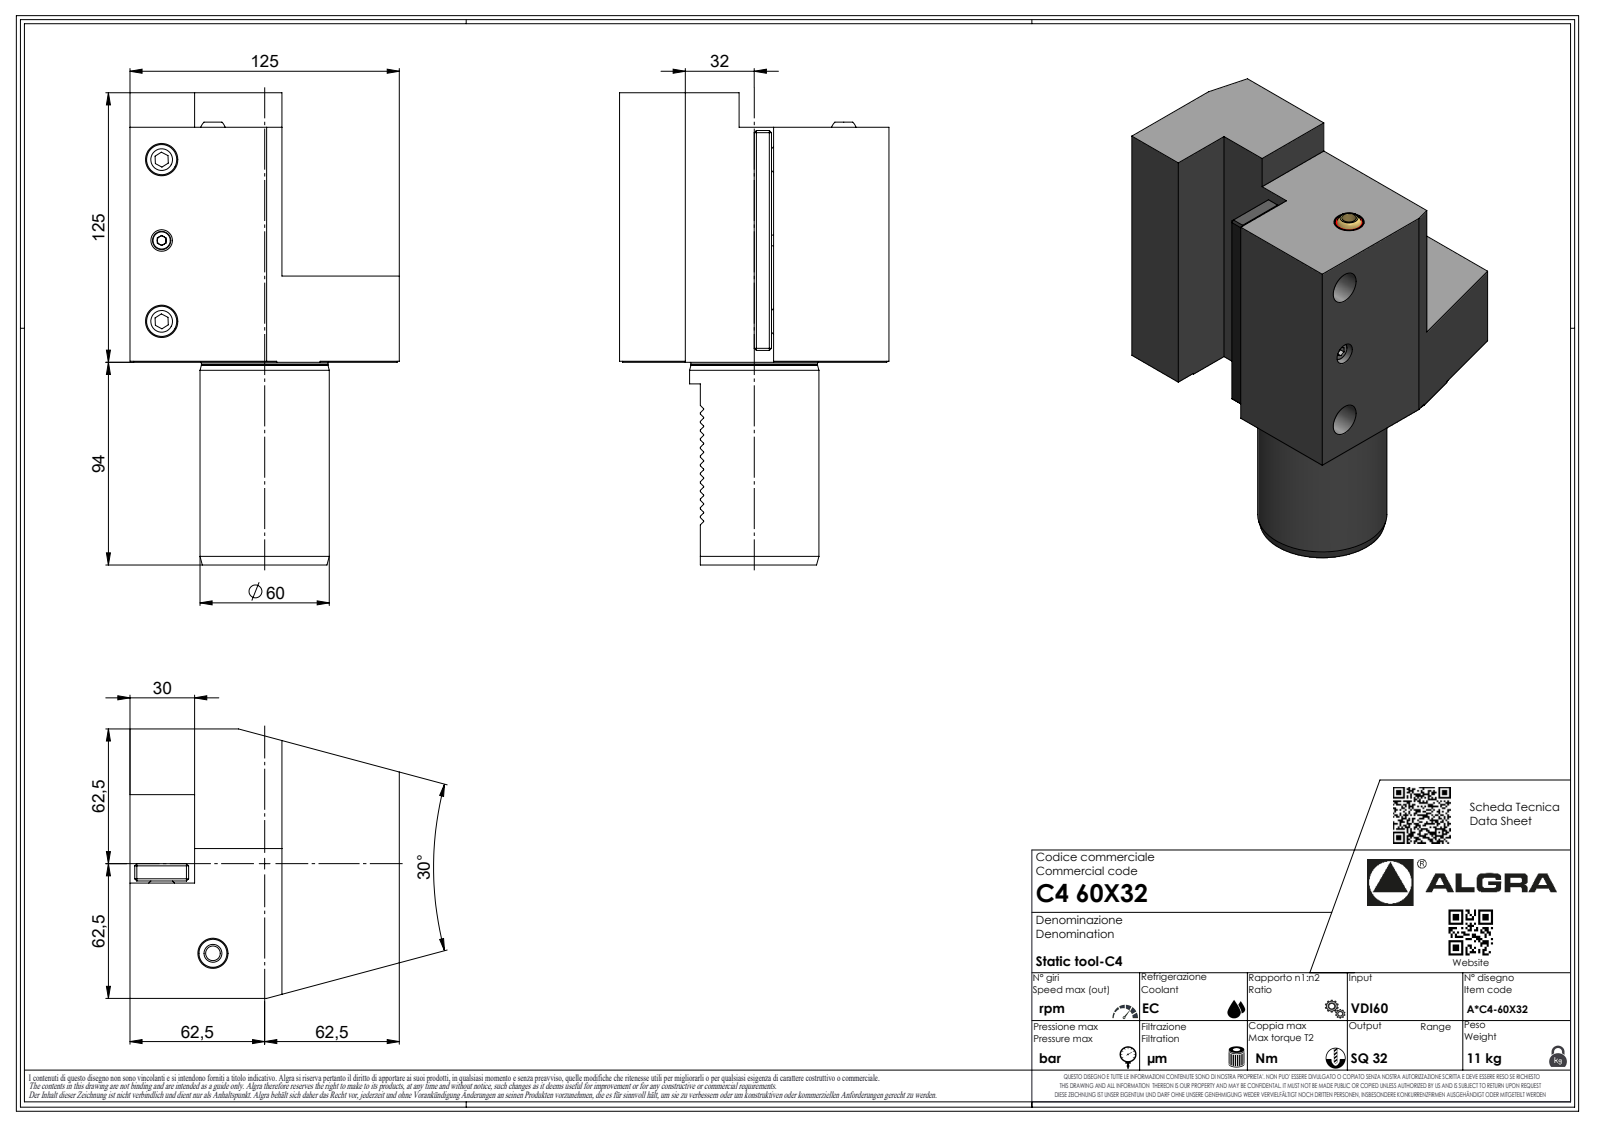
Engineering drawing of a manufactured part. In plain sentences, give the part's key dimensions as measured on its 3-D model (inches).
The part is named "C460X32". Its 3-D file was written by "SolidWorks 2023 (AUTOMOTIVE_DESIGN)". It is 1 solid with 334 faces: 231 planar, 45 cylindrical and 58 other. Overall it measures 8.622 by 4.921 by 4.921 inches. Its volume is 83.6 cubic inches and its surface area 159.2 square inches. Round holes: 1 of diameter 0.083. Round bosses or shafts: 1 of diameter 2.362, 1 of diameter 2.311, 1 of diameter 0.251, 1 of diameter 0.067. Partial cylindrical surfaces (rounded edges, fillets, slot ends): 14 of radius 0.012, 7 of radius 0.013, 7 of radius 0.02, 7 of radius 0.146, 1 of radius 0.008, 1 of radius 2.421. The main face-to-face distances are 4.921, 2.776, 3.72, 1.575, 1.181, 1.594, 2.461, 2.717, 4.291, 0.63.
